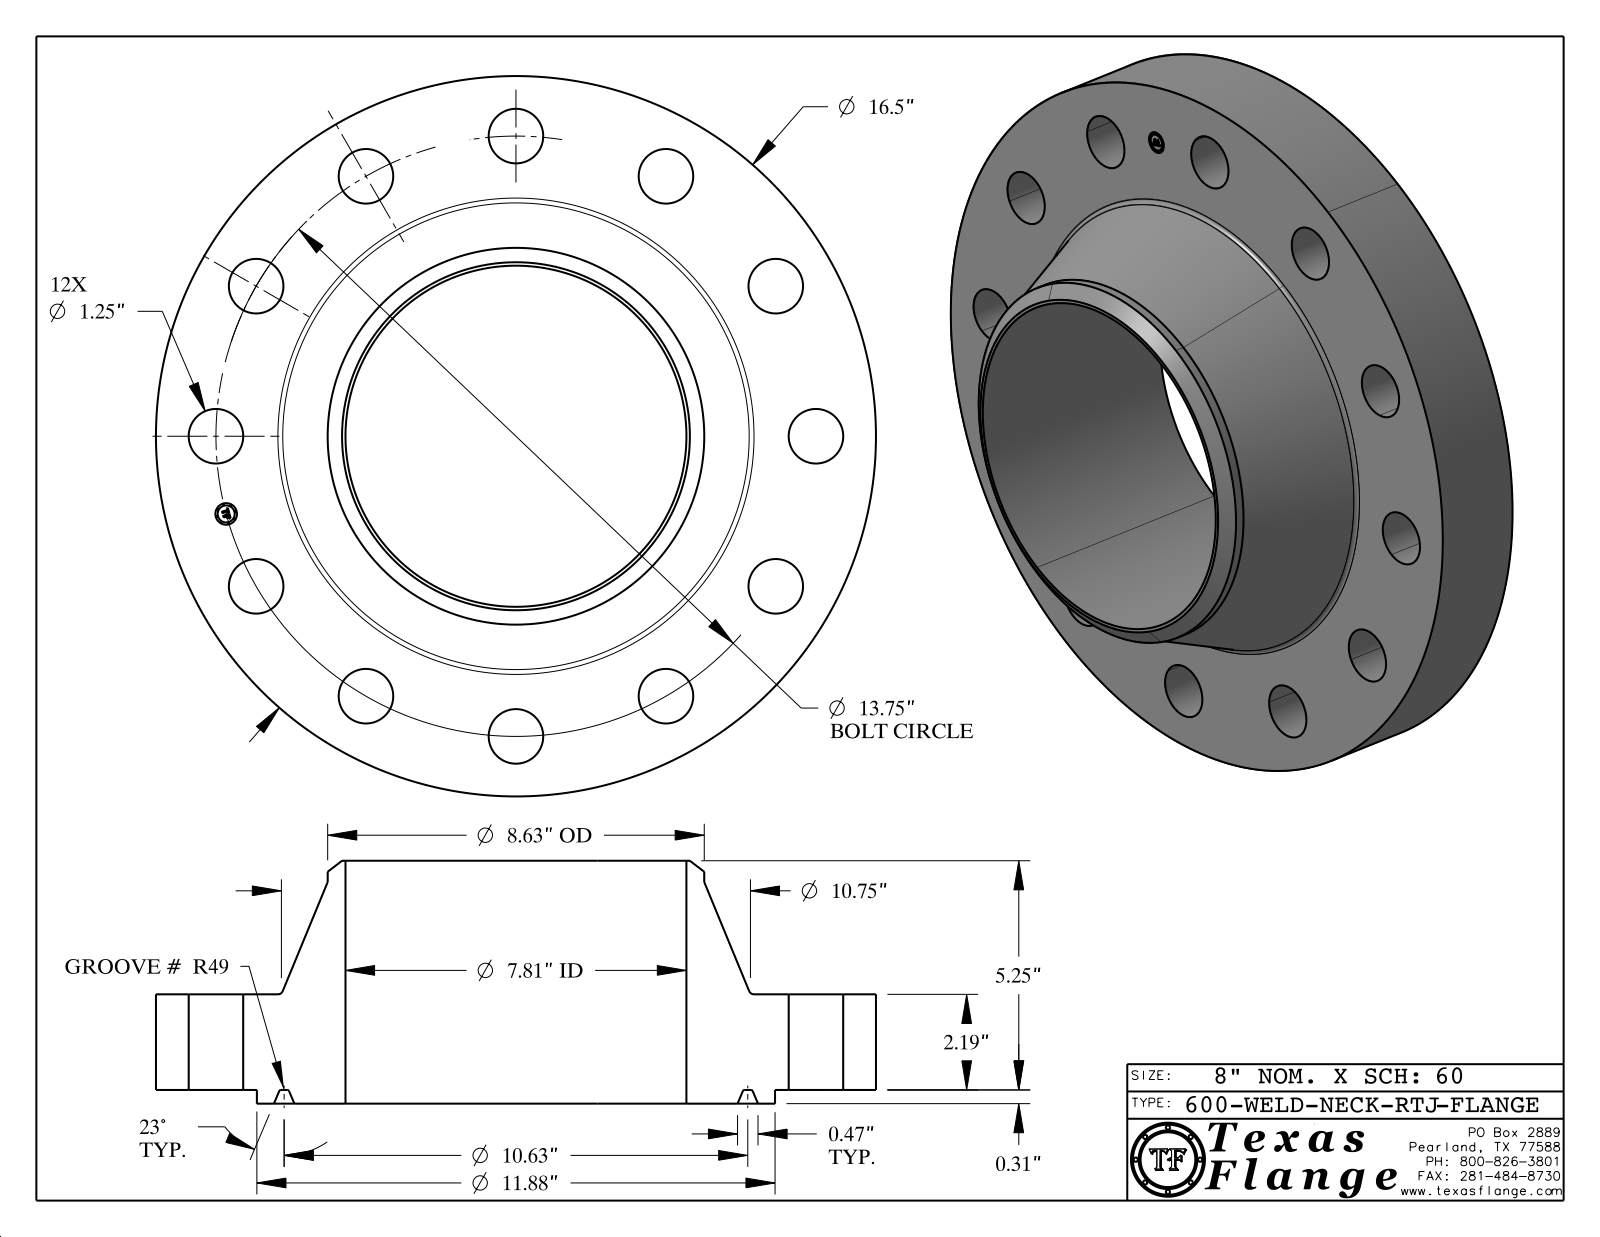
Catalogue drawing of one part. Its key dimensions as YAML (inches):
part_name: "600-WELD-NECK-RTJ"
step_written_by: "CATIA V5 STEP AP214 (AUTOMOTIVE_DESIGN)"
units: inches
bodies: {solids: 1, faces: 437, planar: 371, cylindrical: 52, other: 14}
overall_size: [16.5, 16.5, 5.563]
volume: 418.4
surface_area: 741.2
round_holes:
  - {diameter: 1.25, count: 12}
  - {diameter: 0.495, count: 1}
  - {diameter: 7.813, count: 1}
round_bosses_or_shafts:
  - {diameter: 0.03, count: 8}
  - {diameter: 16.5, count: 1}
  - {diameter: 11.875, count: 1}
  - {diameter: 8.63, count: 1}
  - {diameter: 0.39, count: 1}
face_to_face_distances: [2.19, 0.313, 2.503, 5.563, 5.25, 3.06, 2.488, 2.175, 0.015, 3.075]
hole_center_spacings: [6.875, 6.875, 9.723, 11.908, 13.281, 3.559, 3.559, 13.75]
